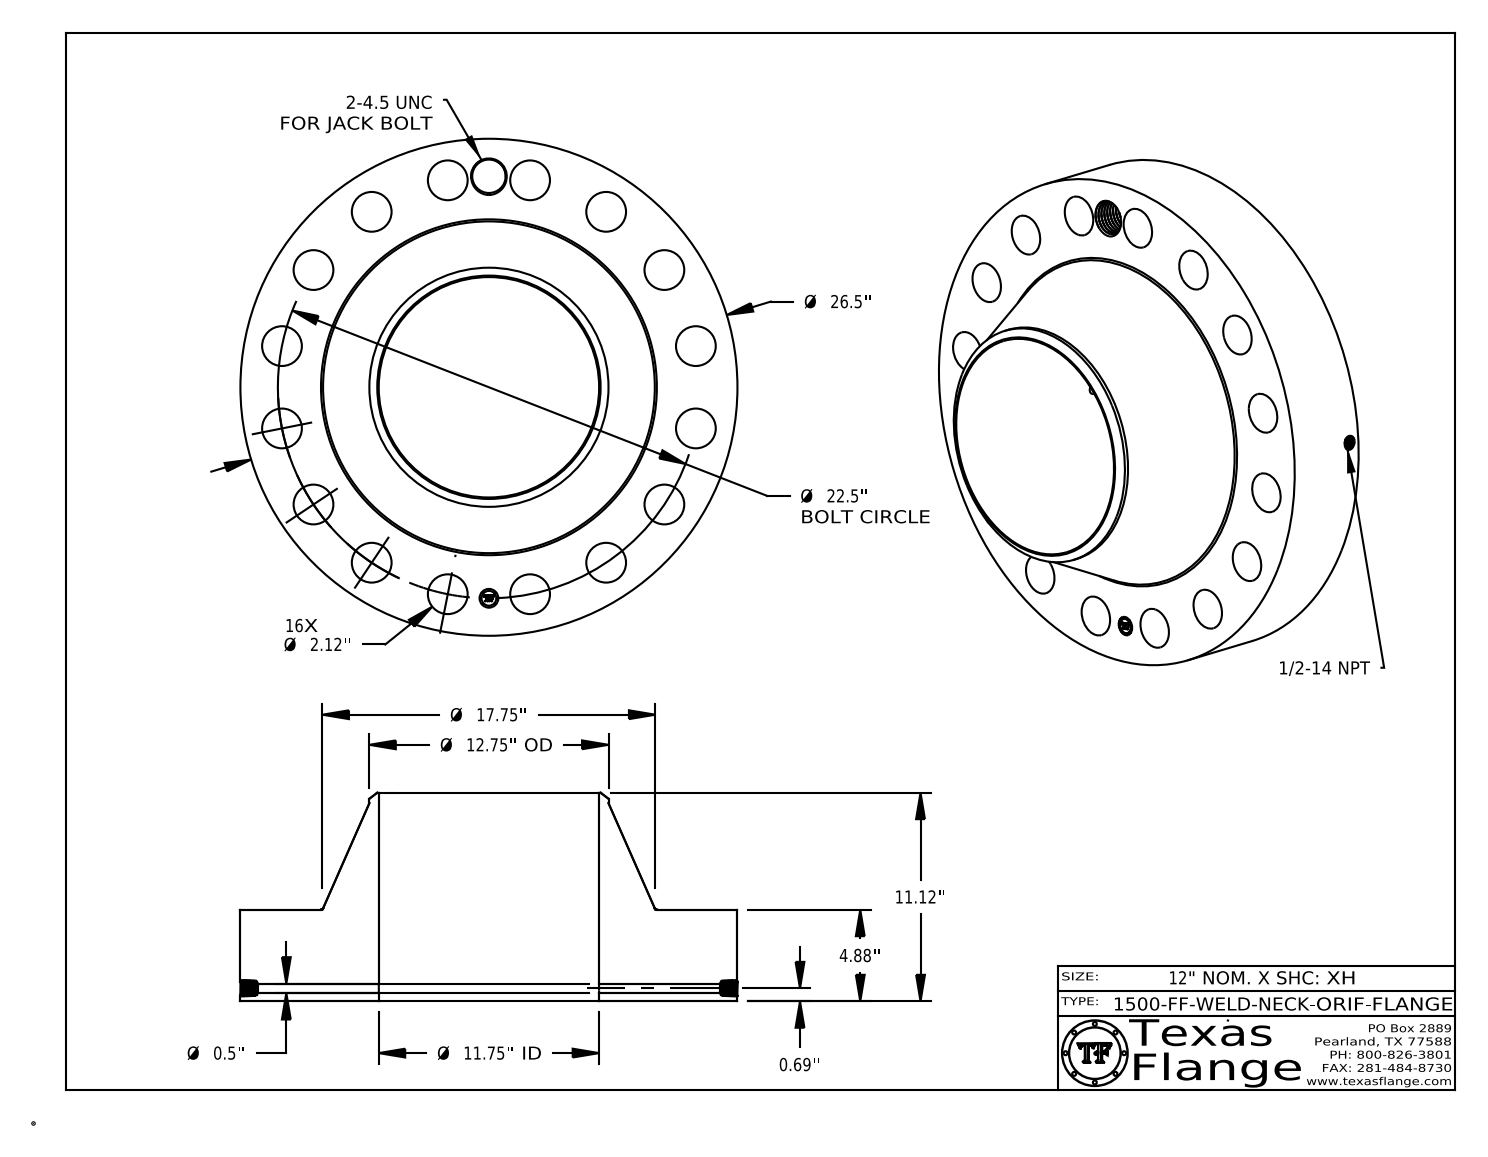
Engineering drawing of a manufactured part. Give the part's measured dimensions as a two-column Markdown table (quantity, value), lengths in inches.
| quantity | value |
| --- | --- |
| part name | 1500-FF-WELD-NECK |
| STEP written by | CATIA V5 STEP AP214 (AUTOMOTIVE_DESIGN) |
| units | inches |
| bodies | 1 solid, 824 faces (368 planar, 122 cylindrical, 334 other) |
| overall size | 26.5 × 26.5 × 11.12 |
| volume | 2 309 in³ |
| surface area | 2 362 in² |
| round holes (diameter × count) | 2.12 × 16, 0.5 × 1, 0.672 × 1, 1 × 1, 1.781 × 1, 11.75 × 1 |
| round bosses / shafts (diameter × count) | 0.061 × 8, 26.5 × 1, 12.75 × 1, 0.788 × 1 |
| main face-to-face distances | 4.88, 11.12, 6.24, 4.865, 0.015, 6.255, 0.298, 0.293, 0.054, 0.248 |
| hole center spacings | 11.25, 8.61, 15.91, 20.787, 12.5, 18.708, 22.068, 4.389 |
